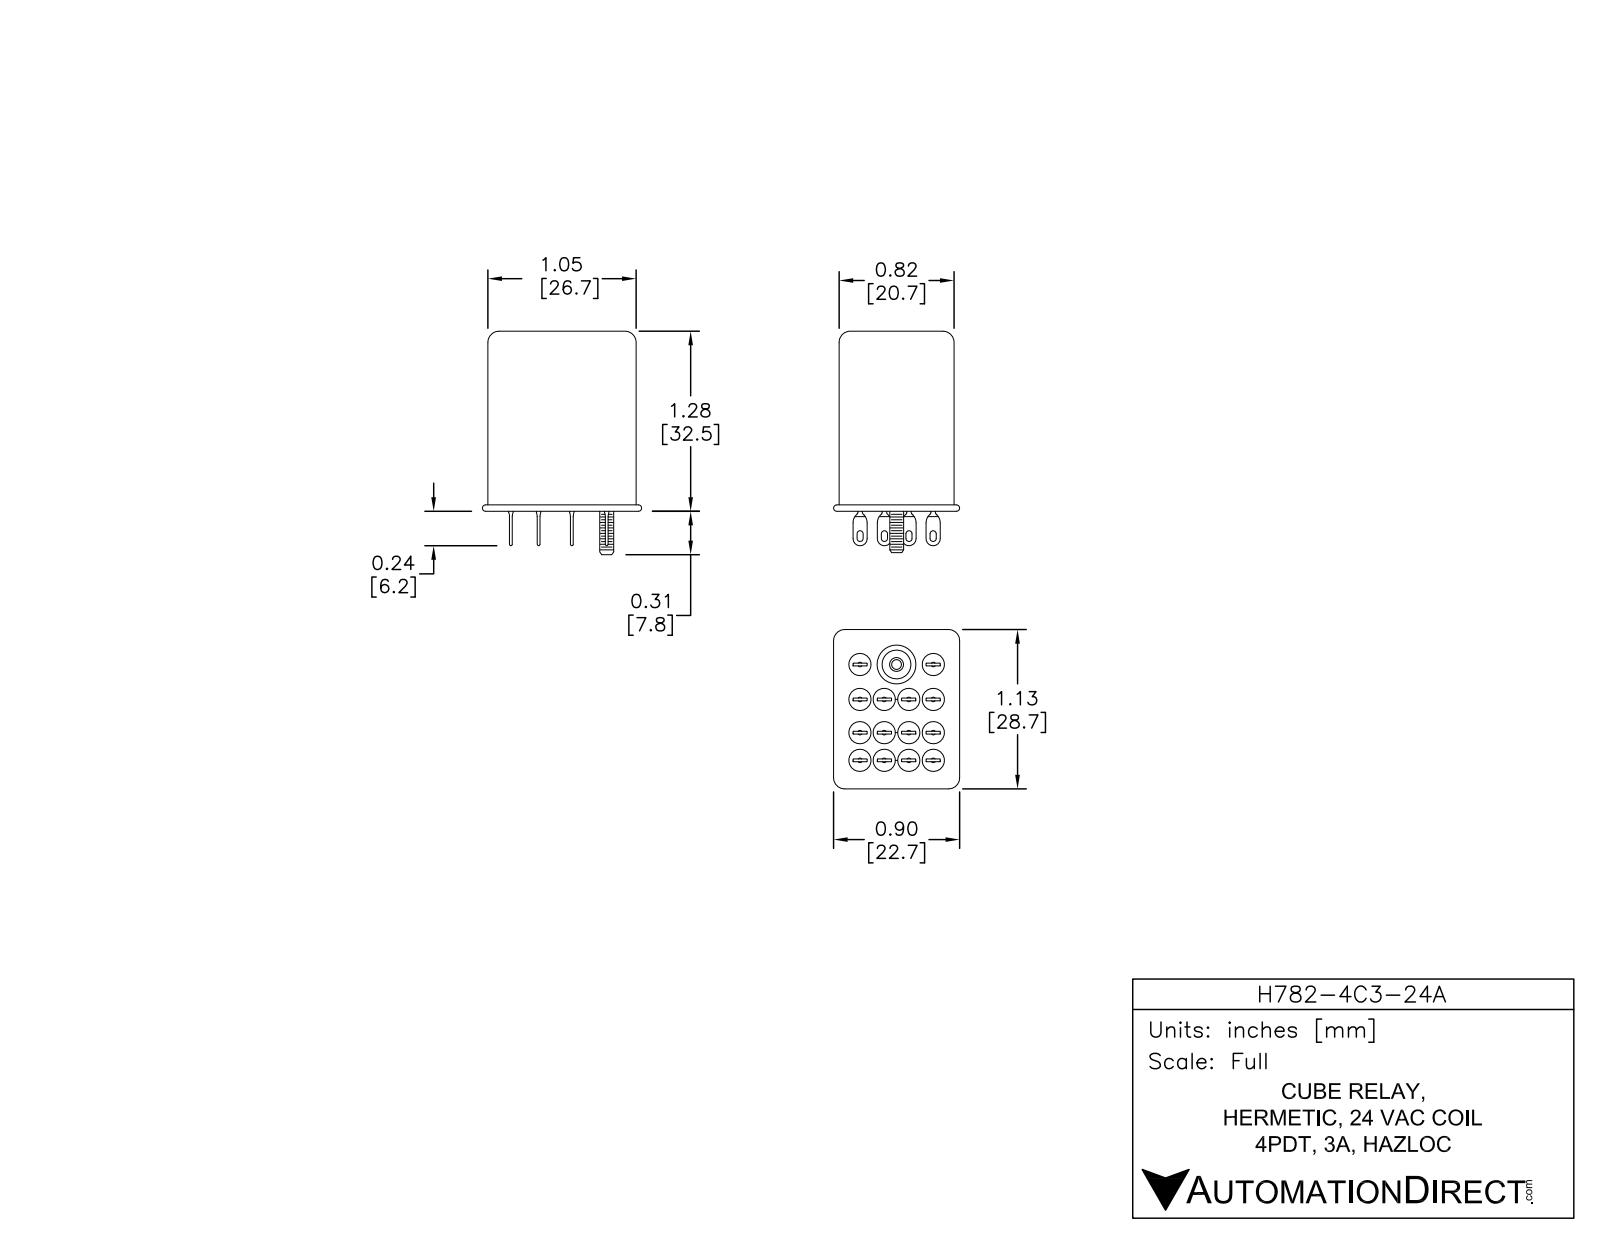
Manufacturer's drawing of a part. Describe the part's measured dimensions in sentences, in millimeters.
The part is named "H782-4C3-24A". Its 3-D file was written by "SolidWorks 2013 (AUTOMOTIVE_DESIGN)". It is 2 solids with 408 faces: 186 planar, 178 cylindrical and 44 other. Overall it measures 35.12 by 28.8 by 22.9 millimeters. Its volume is 15 264 cubic millimeters and its surface area 4 133 square millimeters. Round holes: 1 of diameter 6. Round bosses or shafts: 14 of diameter 3.15, 1 of diameter 2.4. Partial cylindrical surfaces (rounded edges, fillets, slot ends): 56 of radius 0.1, 36 of radius 0.5, 8 of radius 0.2, 4 of radius 2. The main face-to-face distances are 20.5, 27.6, 26.5, 27.62, 5.2, 0.4, 10.4, 10, 4.8, 5.6.
